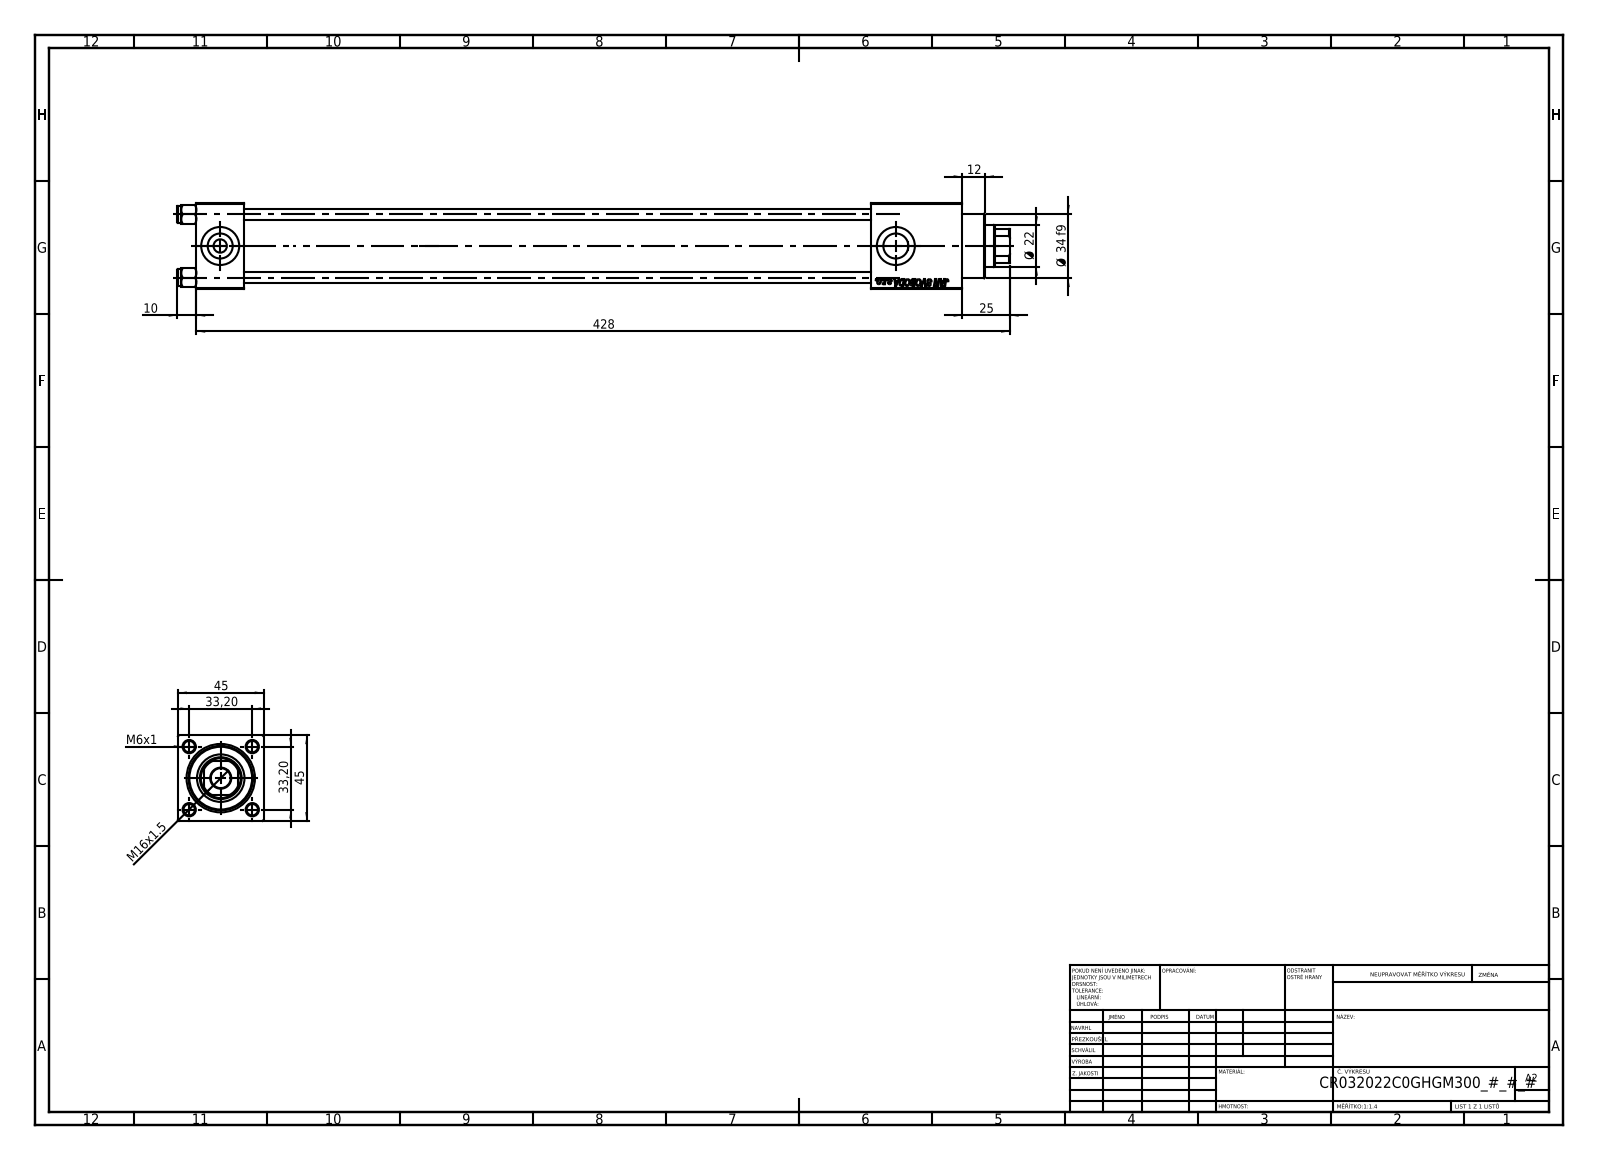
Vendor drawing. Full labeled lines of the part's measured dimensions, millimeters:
Part name (STEP PRODUCT): NUT_M5_C; V215_VC_A; V215CR_C_Body; V215CR_VCP_C (+1 more)
STEP written by: SolidWorks 2019 (CONFIG_CONTROL_DESIGN)
Units: millimetres
Bodies: 11 solids, 1147 faces (525 planar, 86 cylindrical, 536 other)
Overall size (bounding box): 438 × 45 × 45
Volume: 440 327 mm³ · Surface area: 173 341 mm²
Round holes (diameter × count): ⌀6 ×4, ⌀7 ×2, ⌀13.16 ×2, ⌀20 ×2, ⌀10.5 ×1, ⌀22 ×1, ⌀24 ×1, ⌀25 ×1, ⌀32 ×1, ⌀33 ×1
Round bosses / shafts (diameter × count): ⌀9 ×4, ⌀38 ×1, ⌀34 ×1
Partial cylindrical surfaces — rounded edges, fillets, slot ends (radius × count): R10.5 ×1
Main face-to-face distances: 45, 25, 403, 355, 330, 378, 48, 374.3, 349.3, 19.3
Hole centre spacings: 23.48, 33.2, 46.95, 355.5
